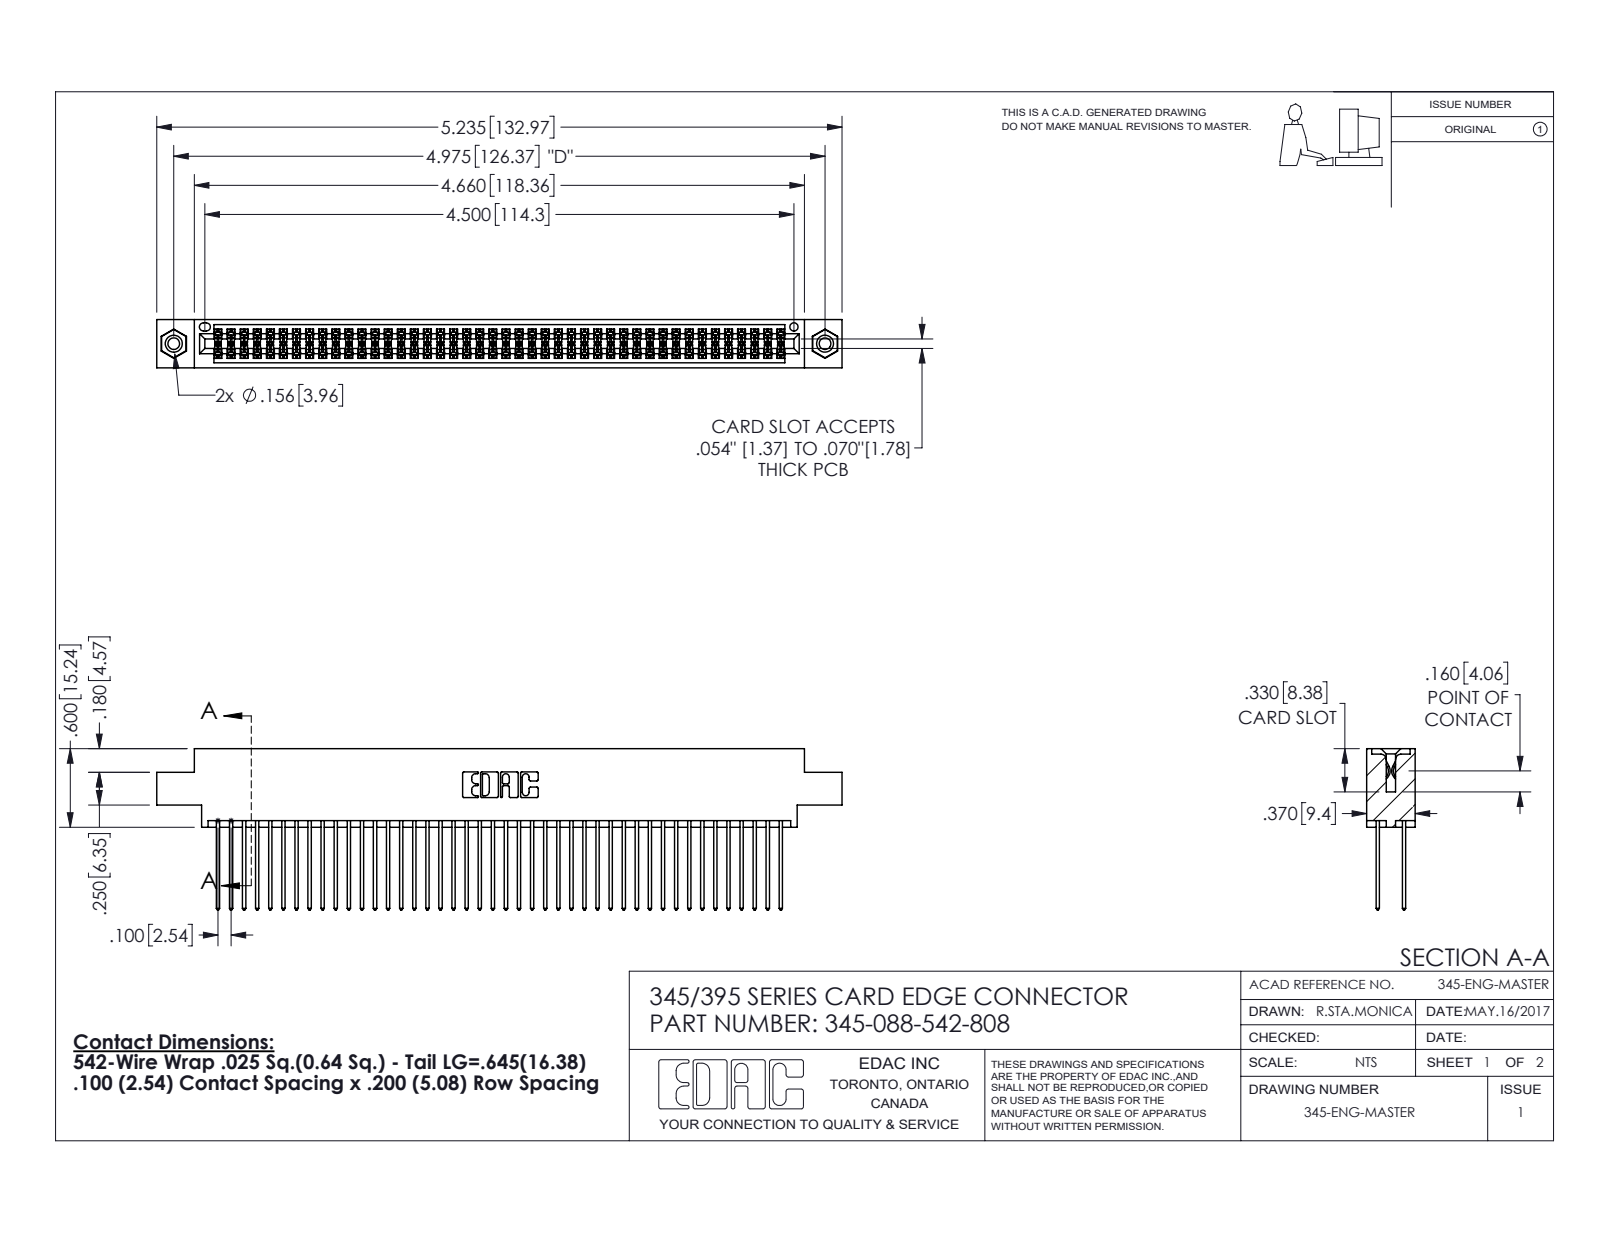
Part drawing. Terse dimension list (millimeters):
name: 345-250-001_345-250-003-102; 345-292-001_345-293-142; 345 Part_0.170 Offset - 0.156 Dia-TI; 345-088-542-808
written by: SolidWorks 2016 (CONFIG_CONTROL_DESIGN)
unit: mm
bodies: 91 solids, 4590 faces (3020 planar, 1554 cylindrical, 16 other)
size: 133 × 31.3 × 9.4
volume: 13 200 mm³; area: 21 660 mm²
holes: 2× ⌀2.3, 2× ⌀3.2, 2× ⌀4, 1× ⌀1.6
bosses: 2× ⌀3.9
rounds: 132× R0.2, 88× R0.3, 22× R0.3, 6× R0.2, 6× R0.8, 3× R0.7, 2× R0.4, 2× R0.5
face distances: 1.8, 7.6, 5.1, 2.5, 6.9, 0.6, 9.4, 5.7, 4.4, 3.8
hole spacings: 6.9, 120.4, 126.4
